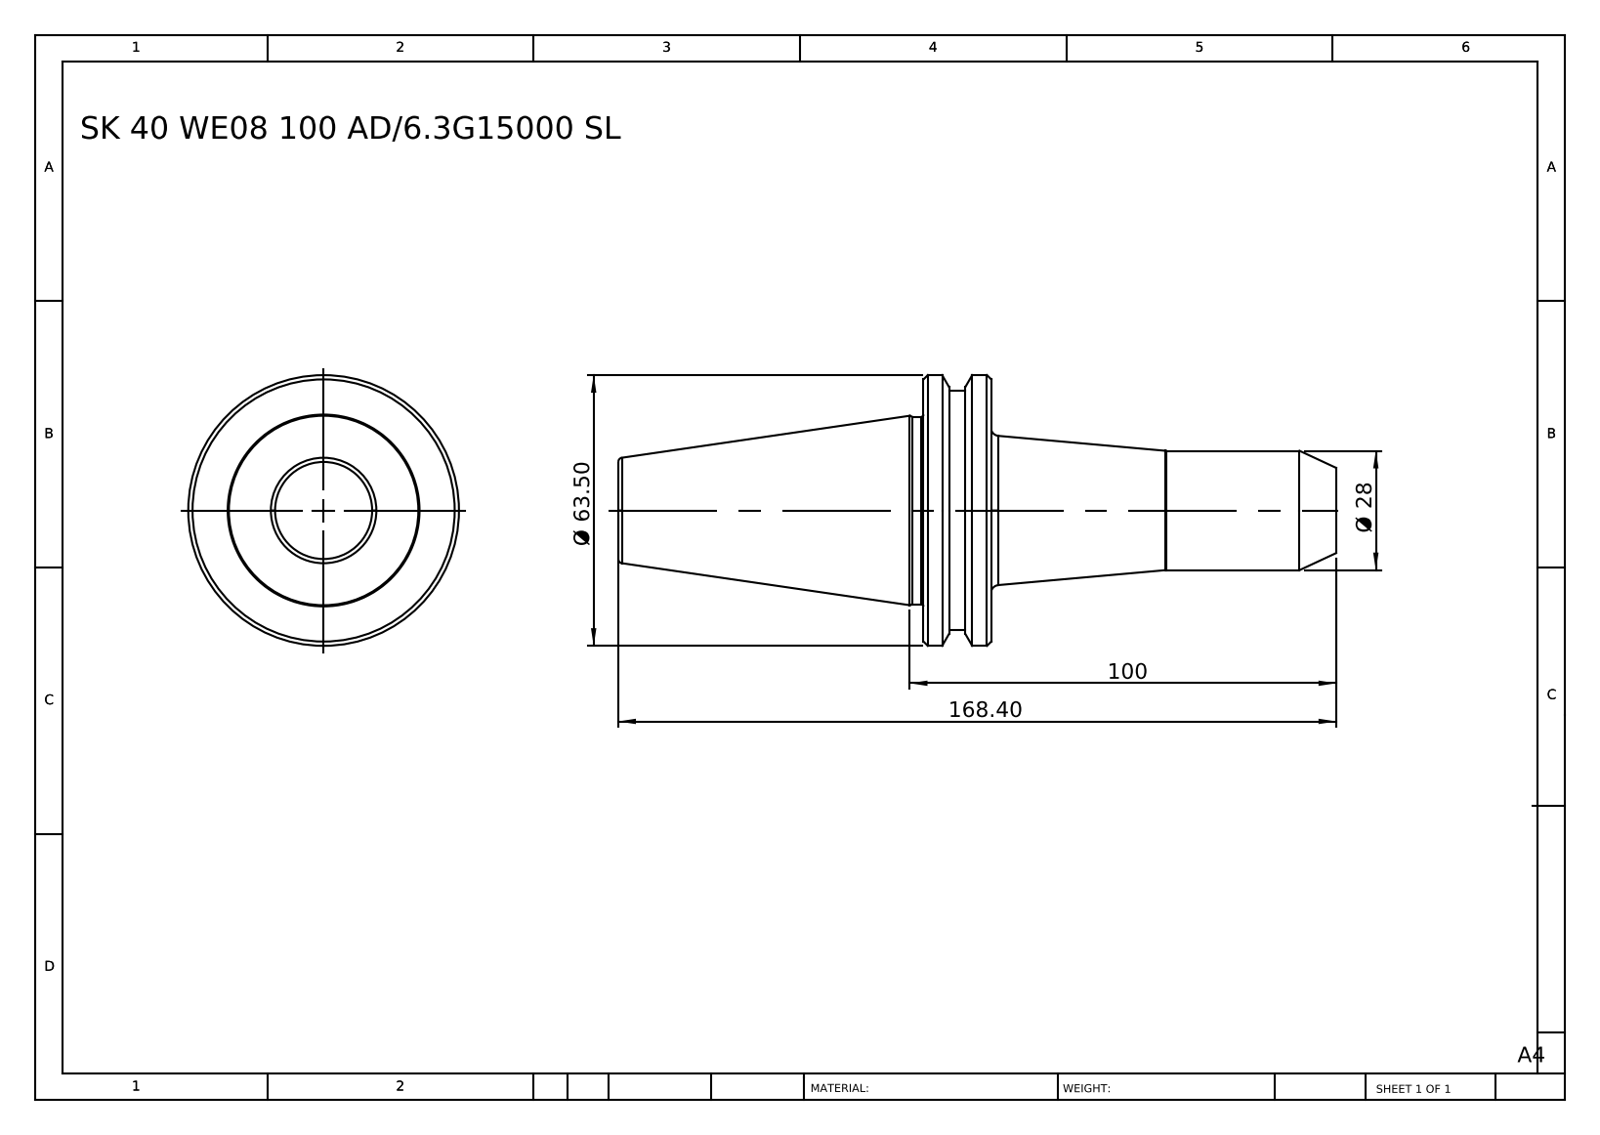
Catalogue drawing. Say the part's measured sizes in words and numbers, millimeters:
The part is named "SK40 WE08 100 AD-6.3G15000 SL". Its 3-D file was written by "SolidWorks 2014 (CONFIG_CONTROL_DESIGN)". It is 1 solid with 40 faces: 6 planar, 10 cylindrical and 24 other. Overall it measures 168.4 by 63.5 by 63.5 millimeters. Its volume is 172 749 cubic millimeters and its surface area 23 770 square millimeters. Round bosses or shafts: 1 of diameter 63.5, 1 of diameter 56, 1 of diameter 44, 1 of diameter 28. The main face-to-face distances are 15.9, 87.5, 71.6, 80.9, 96.8, 168.4, 90.8, 9.9, 6, 77.6.
